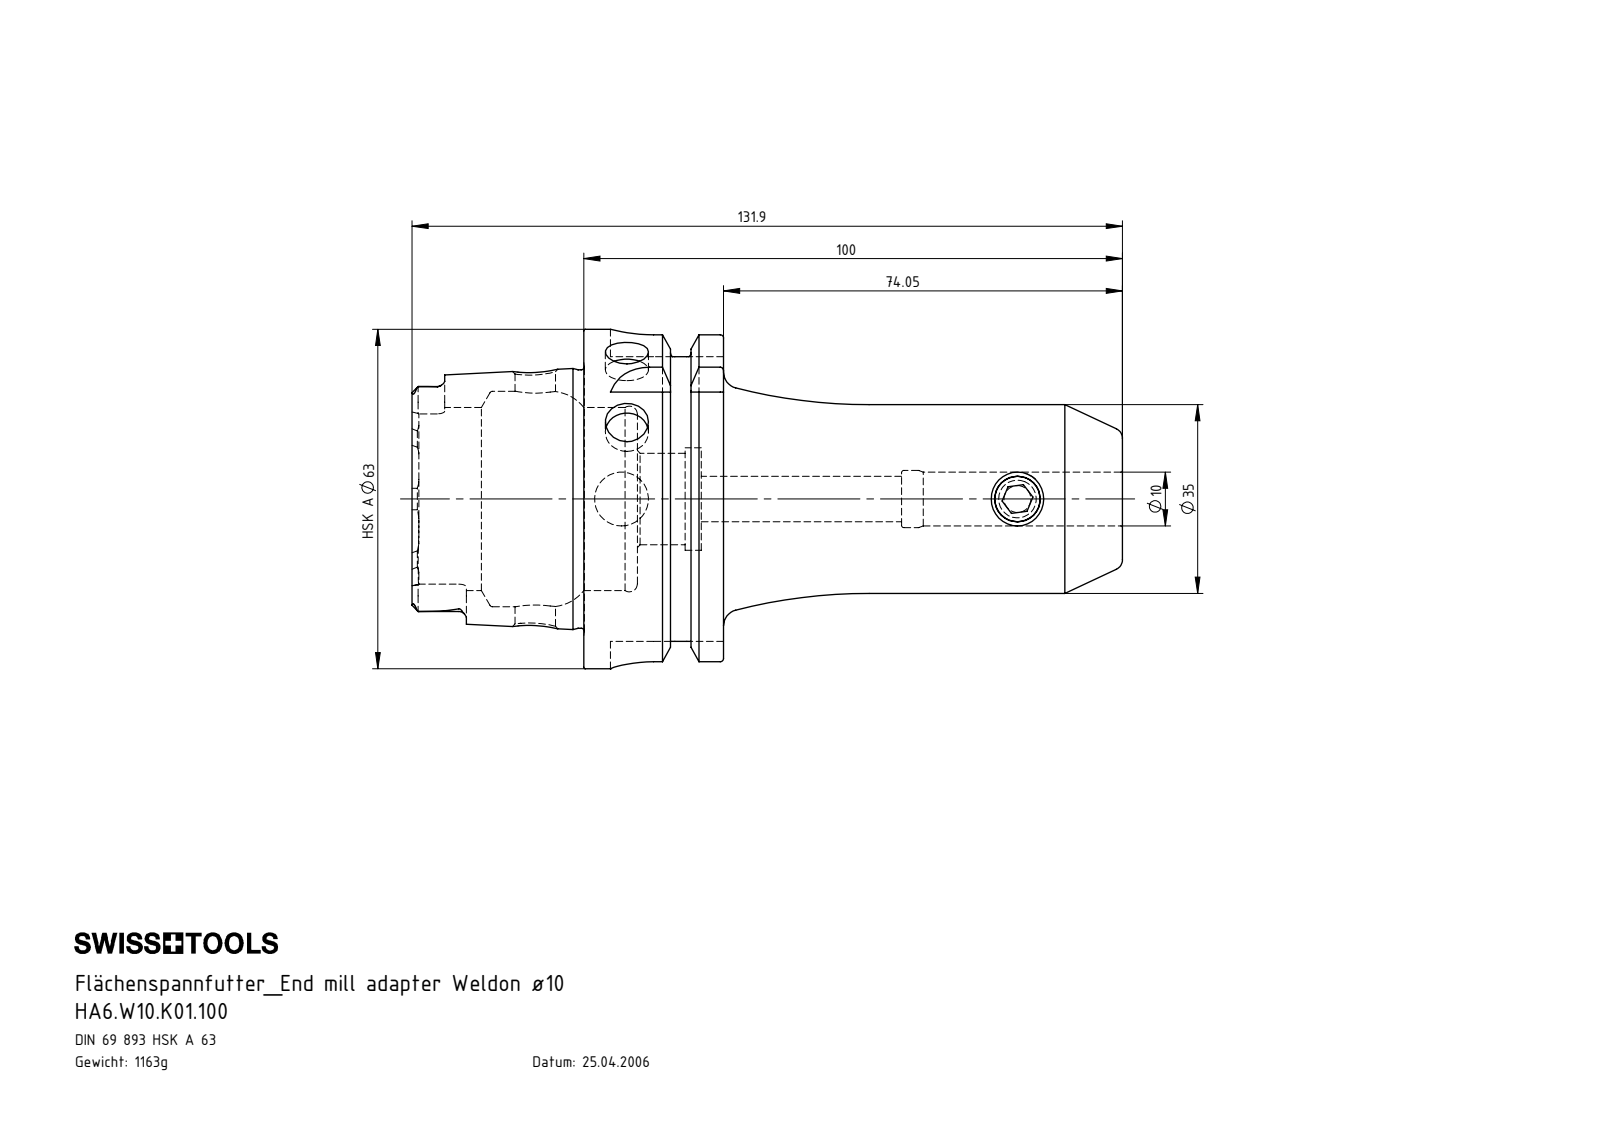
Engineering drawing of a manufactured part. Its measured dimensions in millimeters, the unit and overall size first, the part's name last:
Units: millimetres
Overall size (bounding box): 131.9 × 63 × 63
Round holes (diameter × count): ⌀8 ×2, ⌀10 ×2, ⌀7.5 ×1, ⌀8.4 ×1, ⌀8.5 ×1, ⌀10.6 ×1, ⌀17 ×1, ⌀19 ×1, ⌀34 ×1, ⌀40 ×1
Round bosses / shafts (diameter × count): ⌀63 ×1, ⌀54.95 ×1, ⌀47.94 ×1, ⌀35 ×1, ⌀10 ×1
Partial cylindrical surfaces — rounded edges, fillets, slot ends (radius × count): R1.4 ×6, R2.88 ×4, R8 ×4
Main face-to-face distances: 25.95, 16, 9.95, 31.9, 41.85, 57.85, 131.9, 100, 90.05, 74.05
Hole centre spacings: 73.5
Volume: 148 171 mm³ · Surface area: 32 748 mm²
Bodies: 2 solids, 210 faces (58 planar, 57 cylindrical, 95 other)
Part name (STEP PRODUCT): W10-ER1.001.012; HA6-W10.K01.100; HA6-W10.K01.100_B_Fertigbearbeitung
STEP written by: SolidWorks 2012 (AUTOMOTIVE_DESIGN)
